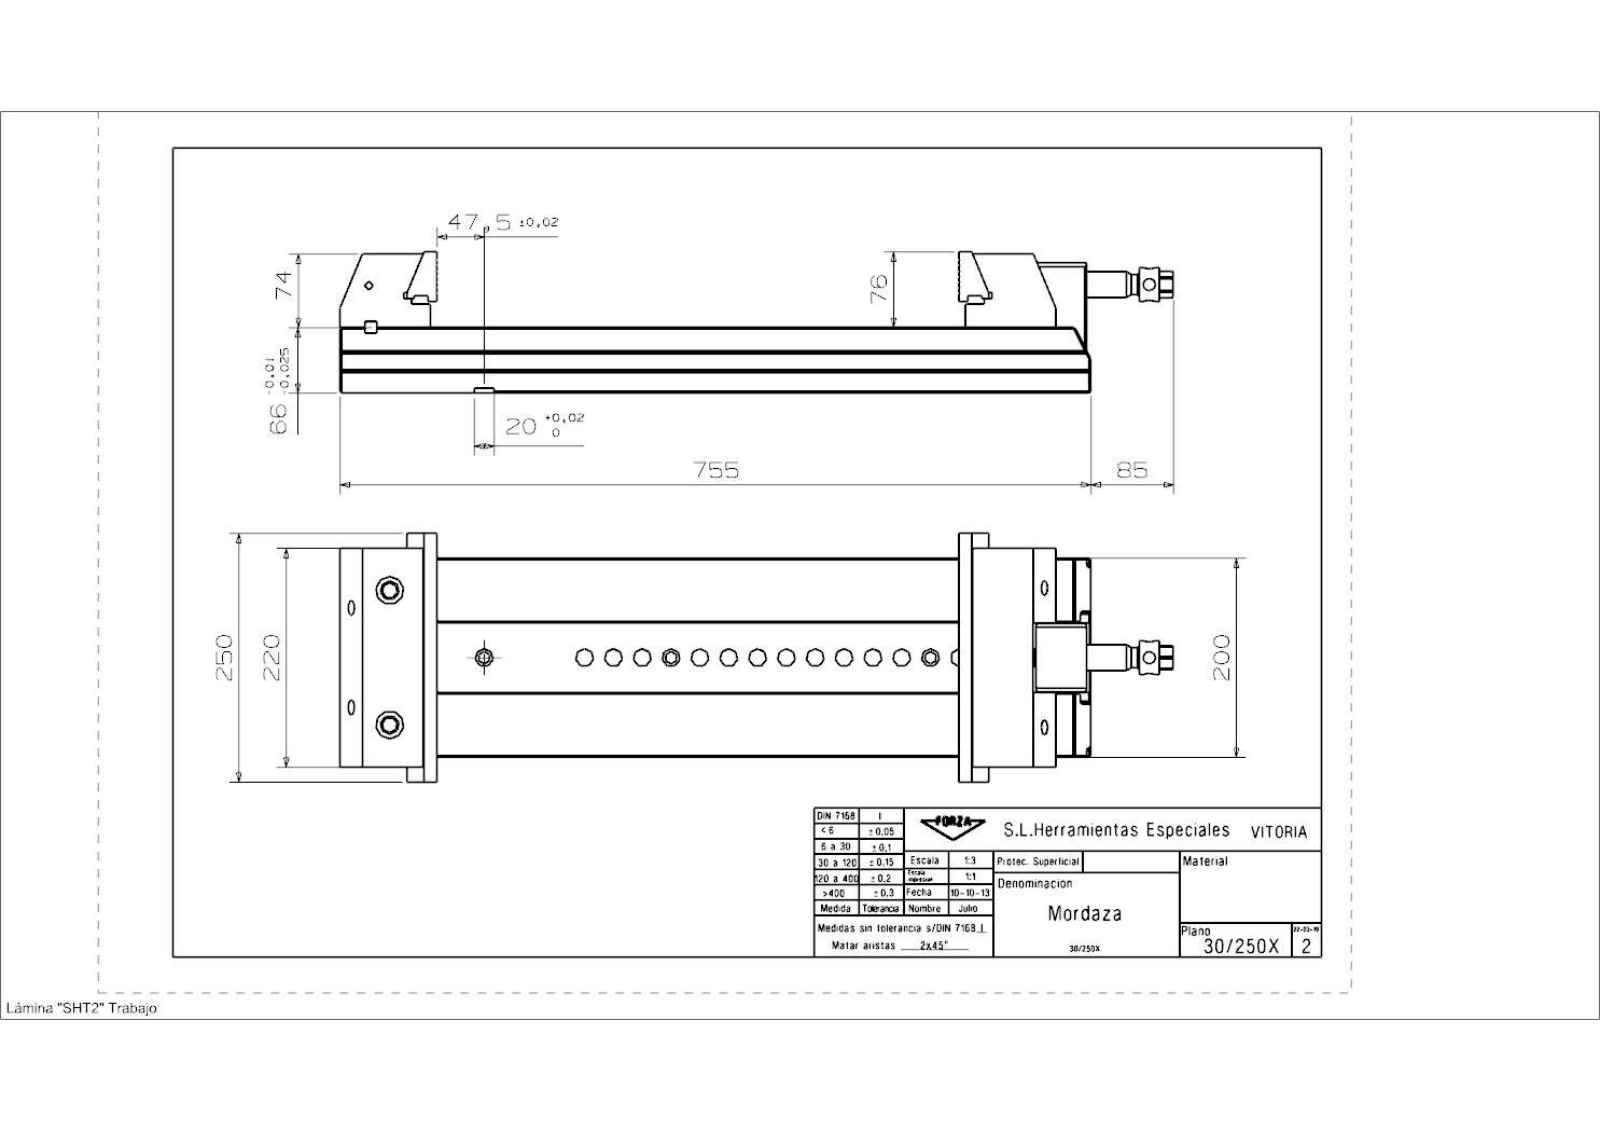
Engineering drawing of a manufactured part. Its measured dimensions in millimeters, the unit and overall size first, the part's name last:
Units: millimetres
Overall size (bounding box): 837.99 × 250 × 142
Round holes (diameter × count): ⌀19 ×5, ⌀5.19 ×4, ⌀9.5 ×4, ⌀15 ×4, ⌀18 ×4, ⌀6 ×3, ⌀8.78 ×3, ⌀10.58 ×3, ⌀12.38 ×3, ⌀13 ×3, ⌀6.5 ×2, ⌀6.99 ×2
Round bosses / shafts (diameter × count): ⌀34 ×1, ⌀33.8 ×1, ⌀26 ×1, ⌀20 ×1, ⌀16.5 ×1
Partial cylindrical surfaces — rounded edges, fillets, slot ends (radius × count): R10 ×8, R6.5 ×2, R9 ×1, R10.5 ×1, R12.5 ×1, R13.25 ×1
Main face-to-face distances: 66, 33.7, 32.3, 1.5, 32.2, 64.5, 145, 65, 10, 200
Hole centre spacings: 20, 22, 27.31, 28.28, 30, 35.38, 46.32, 48.17
Volume: 10 680 000 mm³ · Surface area: 917 472 mm²
Bodies: 13 solids, 635 faces (466 planar, 103 cylindrical, 66 other)
Part name (STEP PRODUCT): 30_250X_Mordaza
STEP written by: SIEMENS PLM Software NX 11.0 (AUTOMOTIVE_DESIGN)
